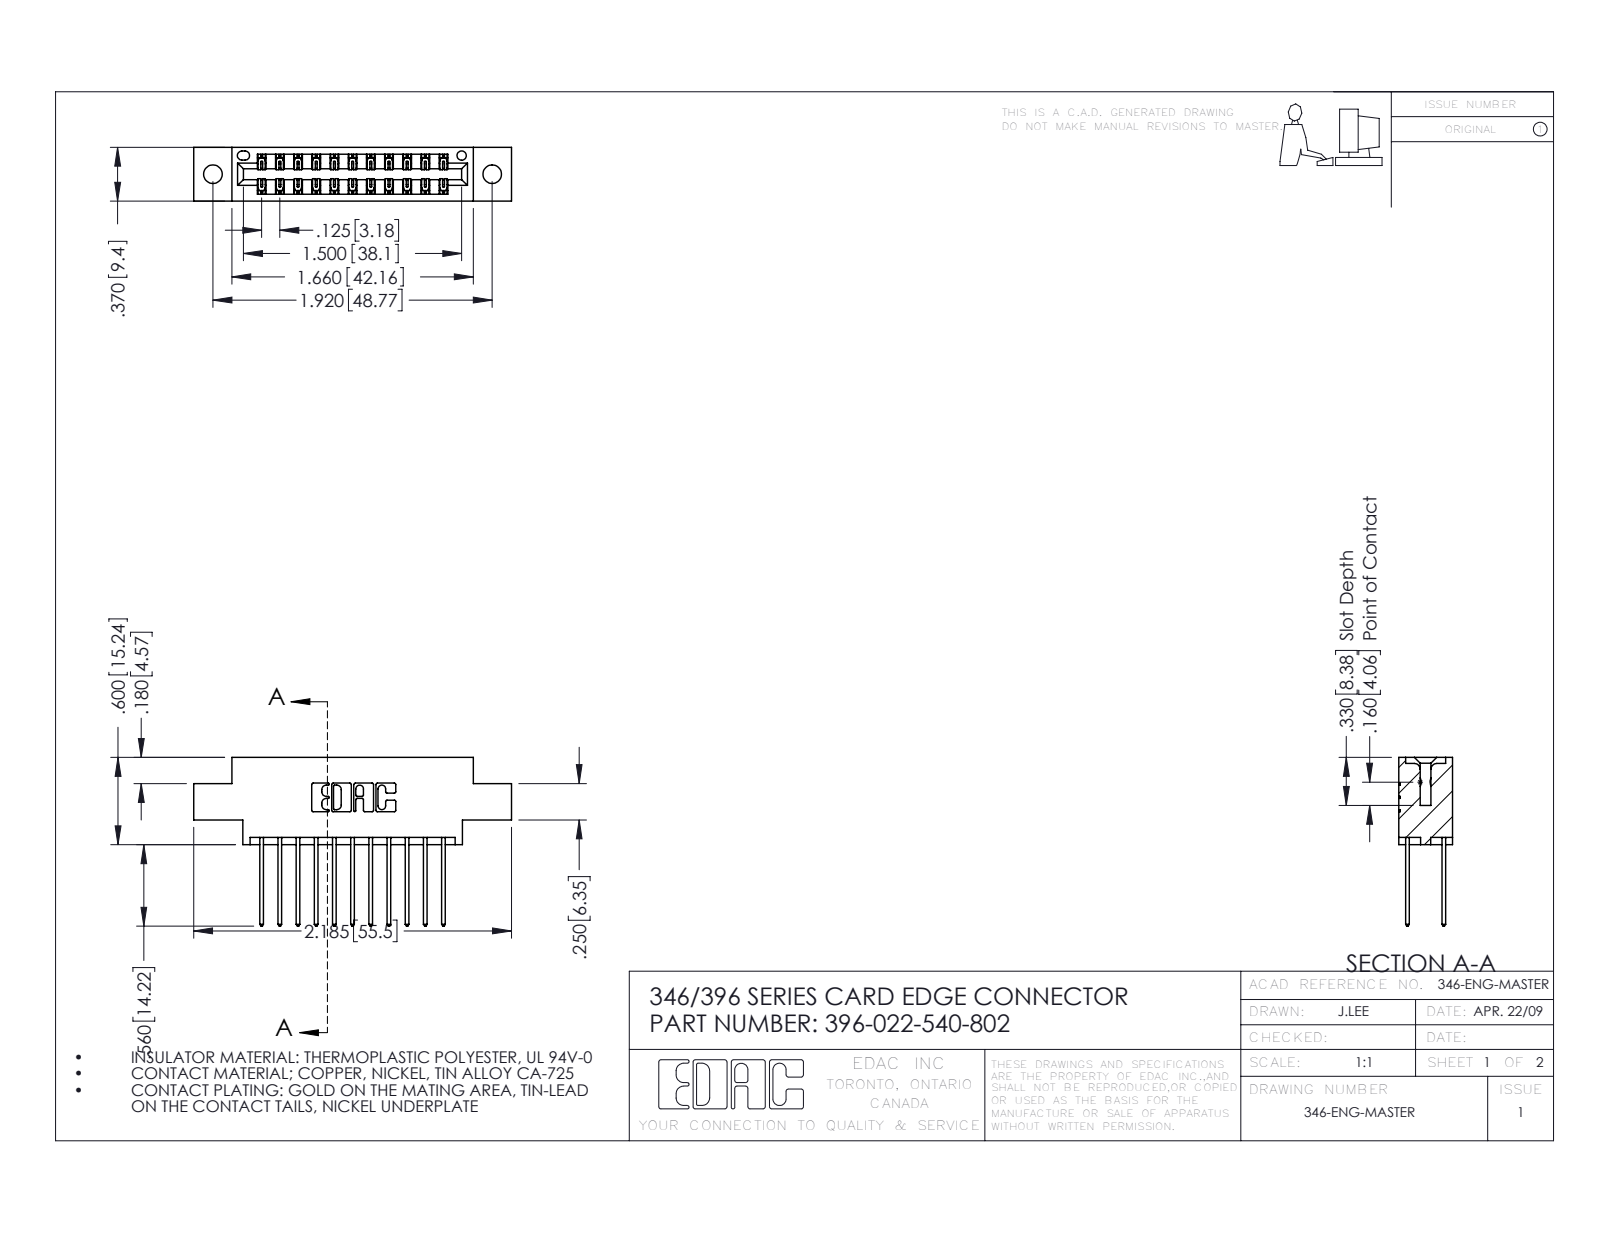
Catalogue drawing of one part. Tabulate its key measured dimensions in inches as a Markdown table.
| quantity | value |
| --- | --- |
| part name | 396-022-540-802; 346 Part_0.170 Offset - 0.128 Dia; 345-292-001_345-293-140 |
| STEP written by | SolidWorks 2016 (CONFIG_CONTROL_DESIGN) |
| units | inches |
| bodies | 23 solids, 1270 faces (850 planar, 420 cylindrical, 0 other) |
| overall size | 2.185 × 1.16 × 0.37 |
| volume | 0.309 in³ |
| surface area | 10.5 in² |
| round holes (diameter × count) | 0.128 × 2, 0.064 × 1 |
| partial cylindrical surfaces (radius × count) | 0.006 × 33, 0.01 × 22, 0.01 × 22, 0.007 × 6, 0.031 × 6, 0.026 × 3, 0.014 × 2, 0.022 × 2 |
| main face-to-face distances | 0.25, 0.048, 0.322, 0.37, 0.072, 0.298, 0.025, 0.275, 0.148, 0.222 |
| hole center spacings | 0.246, 1.715, 1.92 |
